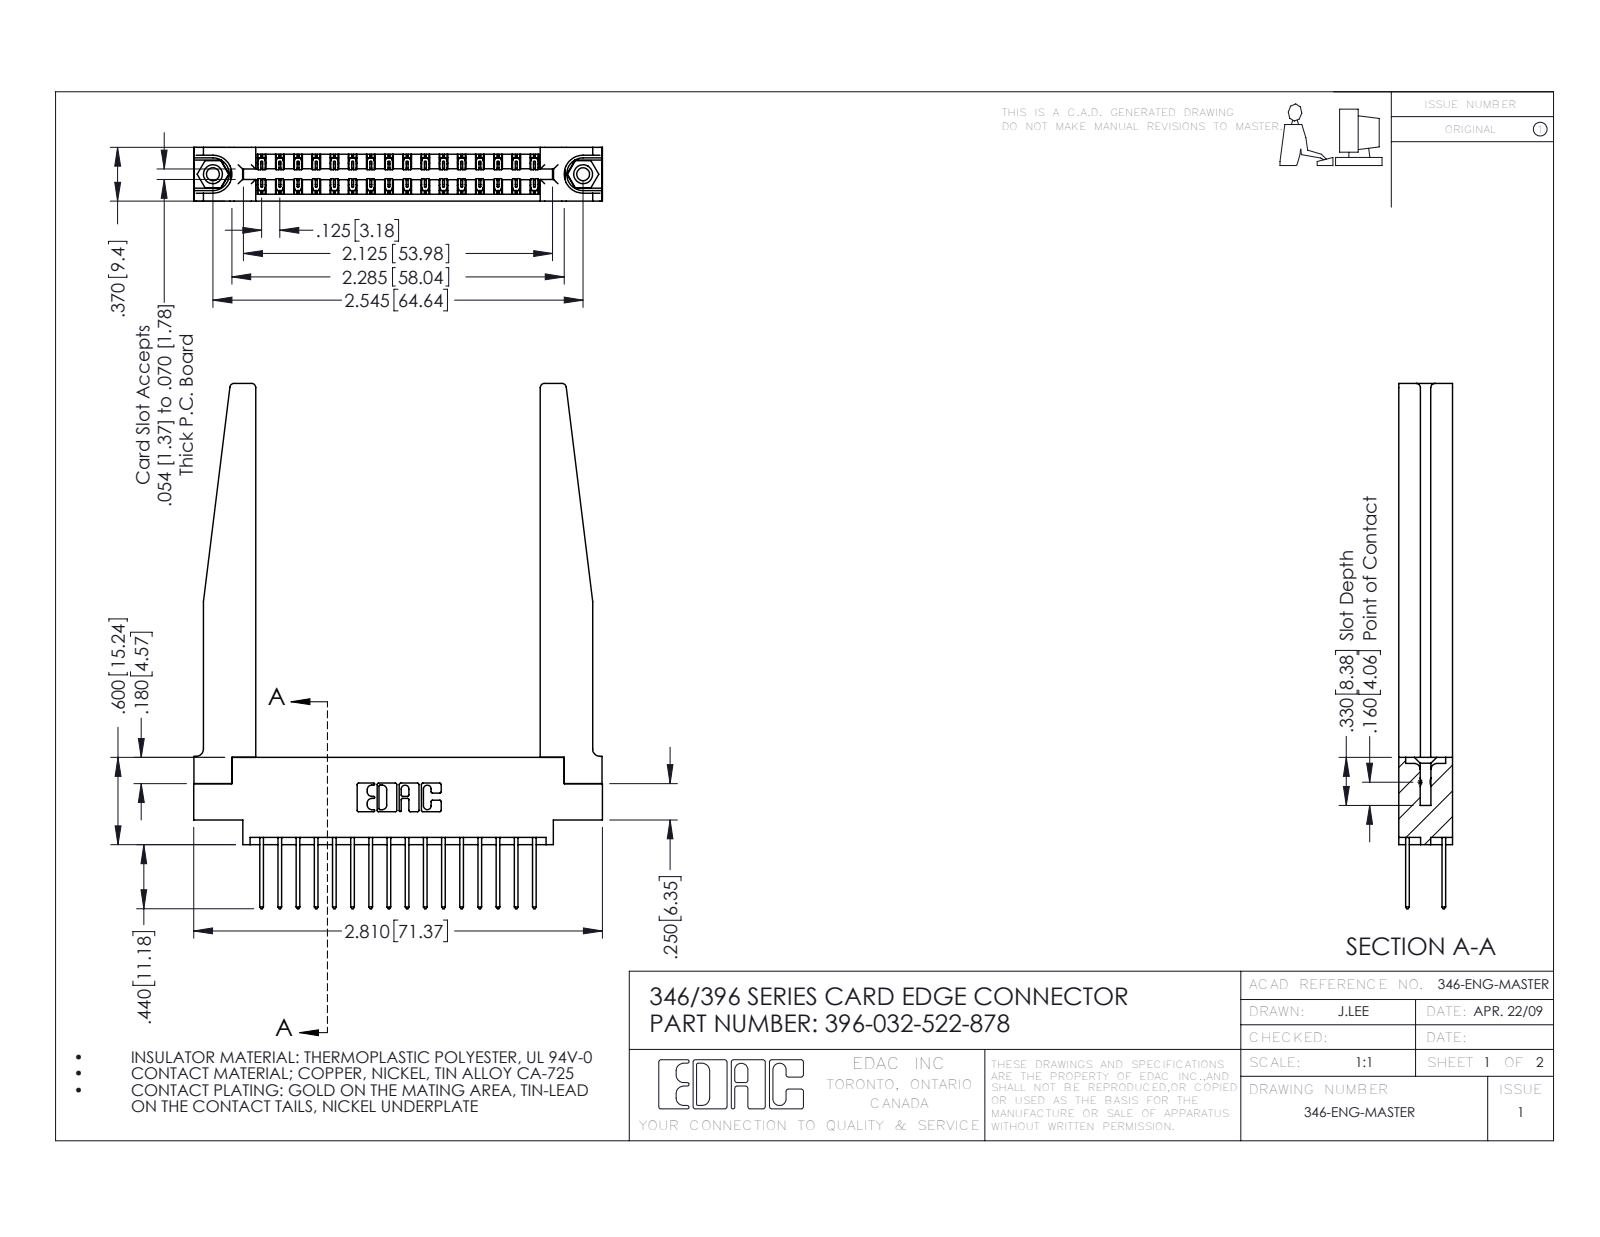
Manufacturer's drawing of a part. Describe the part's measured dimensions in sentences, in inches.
The part is named "346-220-078_345-220-078; 345-292-001_345-293-122; 346 Part_0.170 Offset - 0.156 Dia-TH; 396-032-522-878 (+1 more)". Its 3-D file was written by "SolidWorks 2016 (CONFIG_CONTROL_DESIGN)". It is 37 solids with 2024 faces: 1342 planar, 630 cylindrical and 52 other. Overall it measures 3.61 by 2.81 by 0.37 inches. Its volume is 0.83 cubic inches and its surface area 24.61 square inches. Round holes: 2 of diameter 0.089, 2 of diameter 0.125, 2 of diameter 0.156, 1 of diameter 0.064. Round bosses or shafts: 2 of diameter 0.155. Partial cylindrical surfaces (rounded edges, fillets, slot ends): 48 of radius 0.006, 32 of radius 0.01, 22 of radius 0.01, 8 of radius 0.03, 6 of radius 0.007, 6 of radius 0.031, 3 of radius 0.026, 2 of radius 0.014. The main face-to-face distances are 0.37, 0.072, 0.048, 0.322, 0.148, 0.15, 0.25, 0.298, 0.025, 0.275. The hole center spacings are 0.246, 2.338, 2.545.
